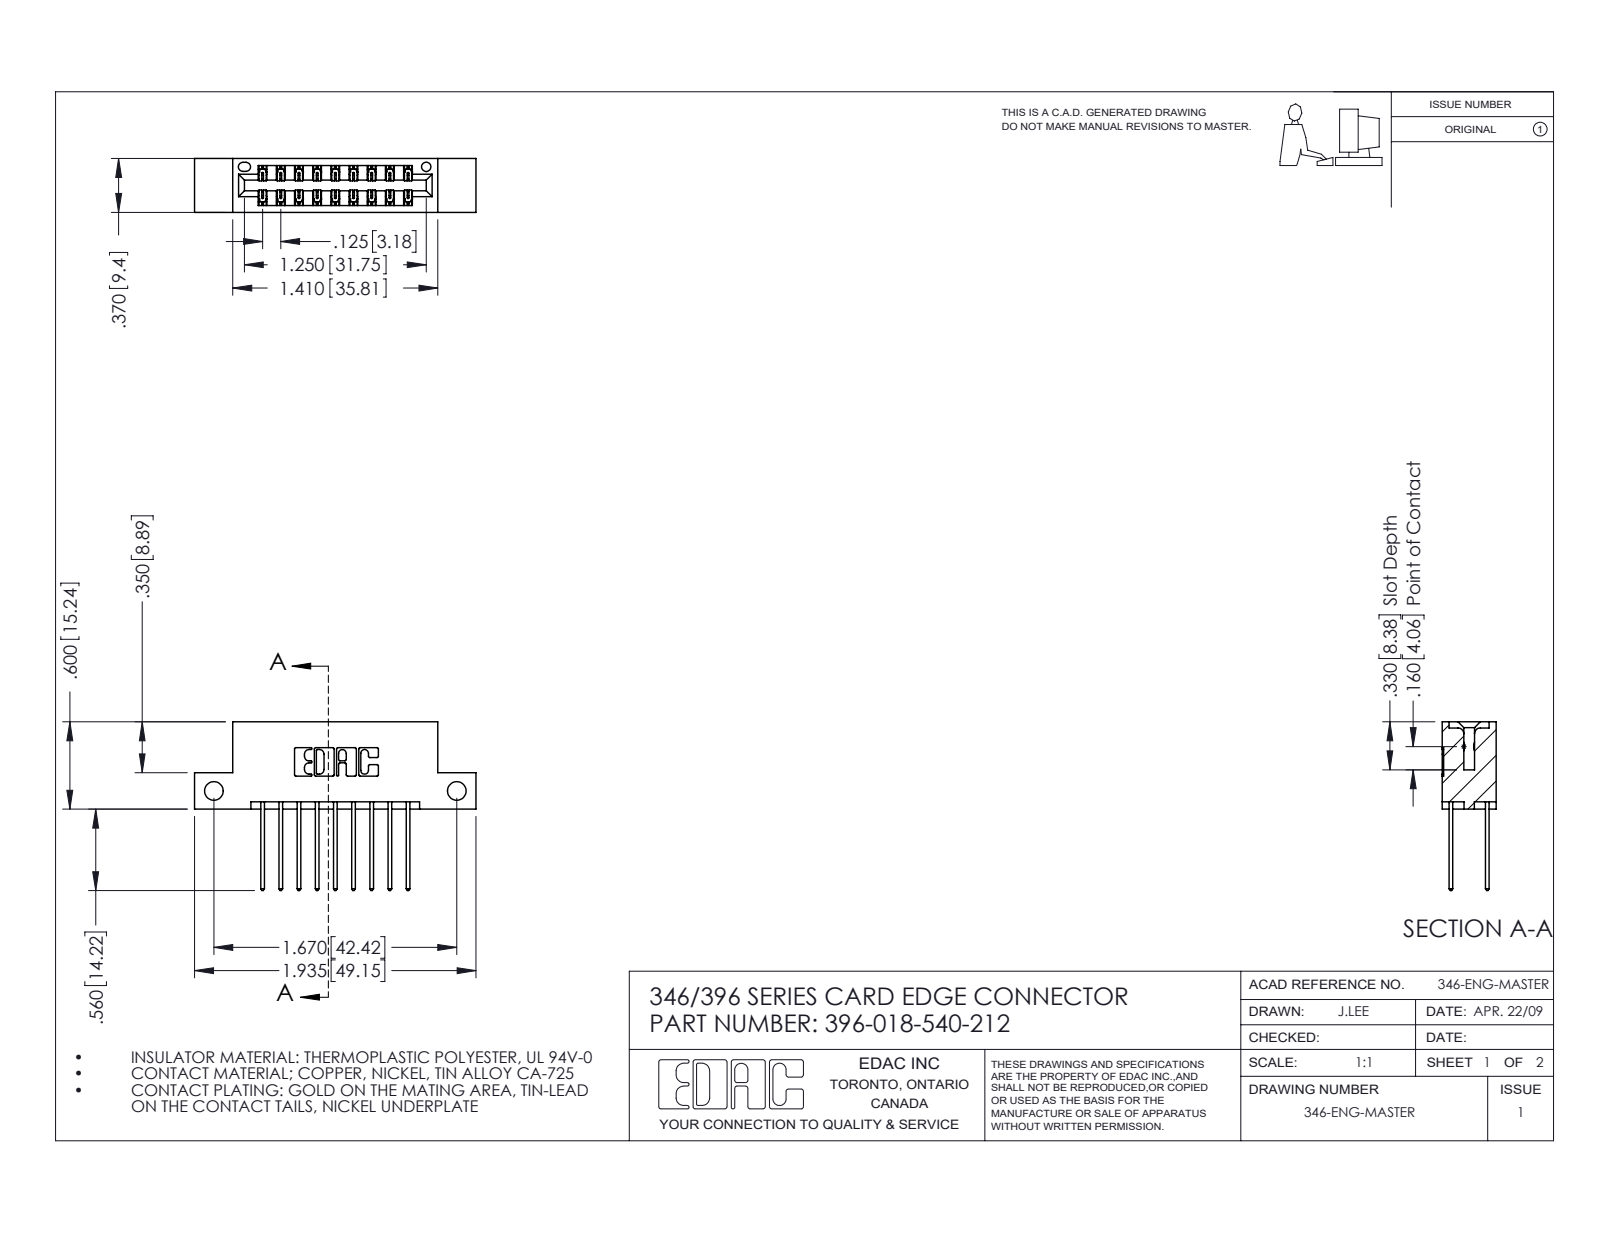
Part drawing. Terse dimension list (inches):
name: 396-018-540-212; 345-292-001_345-293-140; 346 Part_Flush Mounting Lugs - Side Mount
written by: SolidWorks 2016 (CONFIG_CONTROL_DESIGN)
unit: in
bodies: 19 solids, 1058 faces (706 planar, 352 cylindrical, 0 other)
size: 1.935 × 1.16 × 0.37
volume: 0.276 in³; area: 9.108 in²
holes: 2× ⌀0.128, 1× ⌀0.064
rounds: 27× R0.006, 22× R0.01, 18× R0.01, 6× R0.007, 6× R0.031, 3× R0.026, 2× R0.014, 2× R0.022
face distances: 0.25, 0.048, 0.322, 0.37, 0.072, 0.298, 0.025, 0.275, 0.148, 0.222
hole spacings: 1.67
